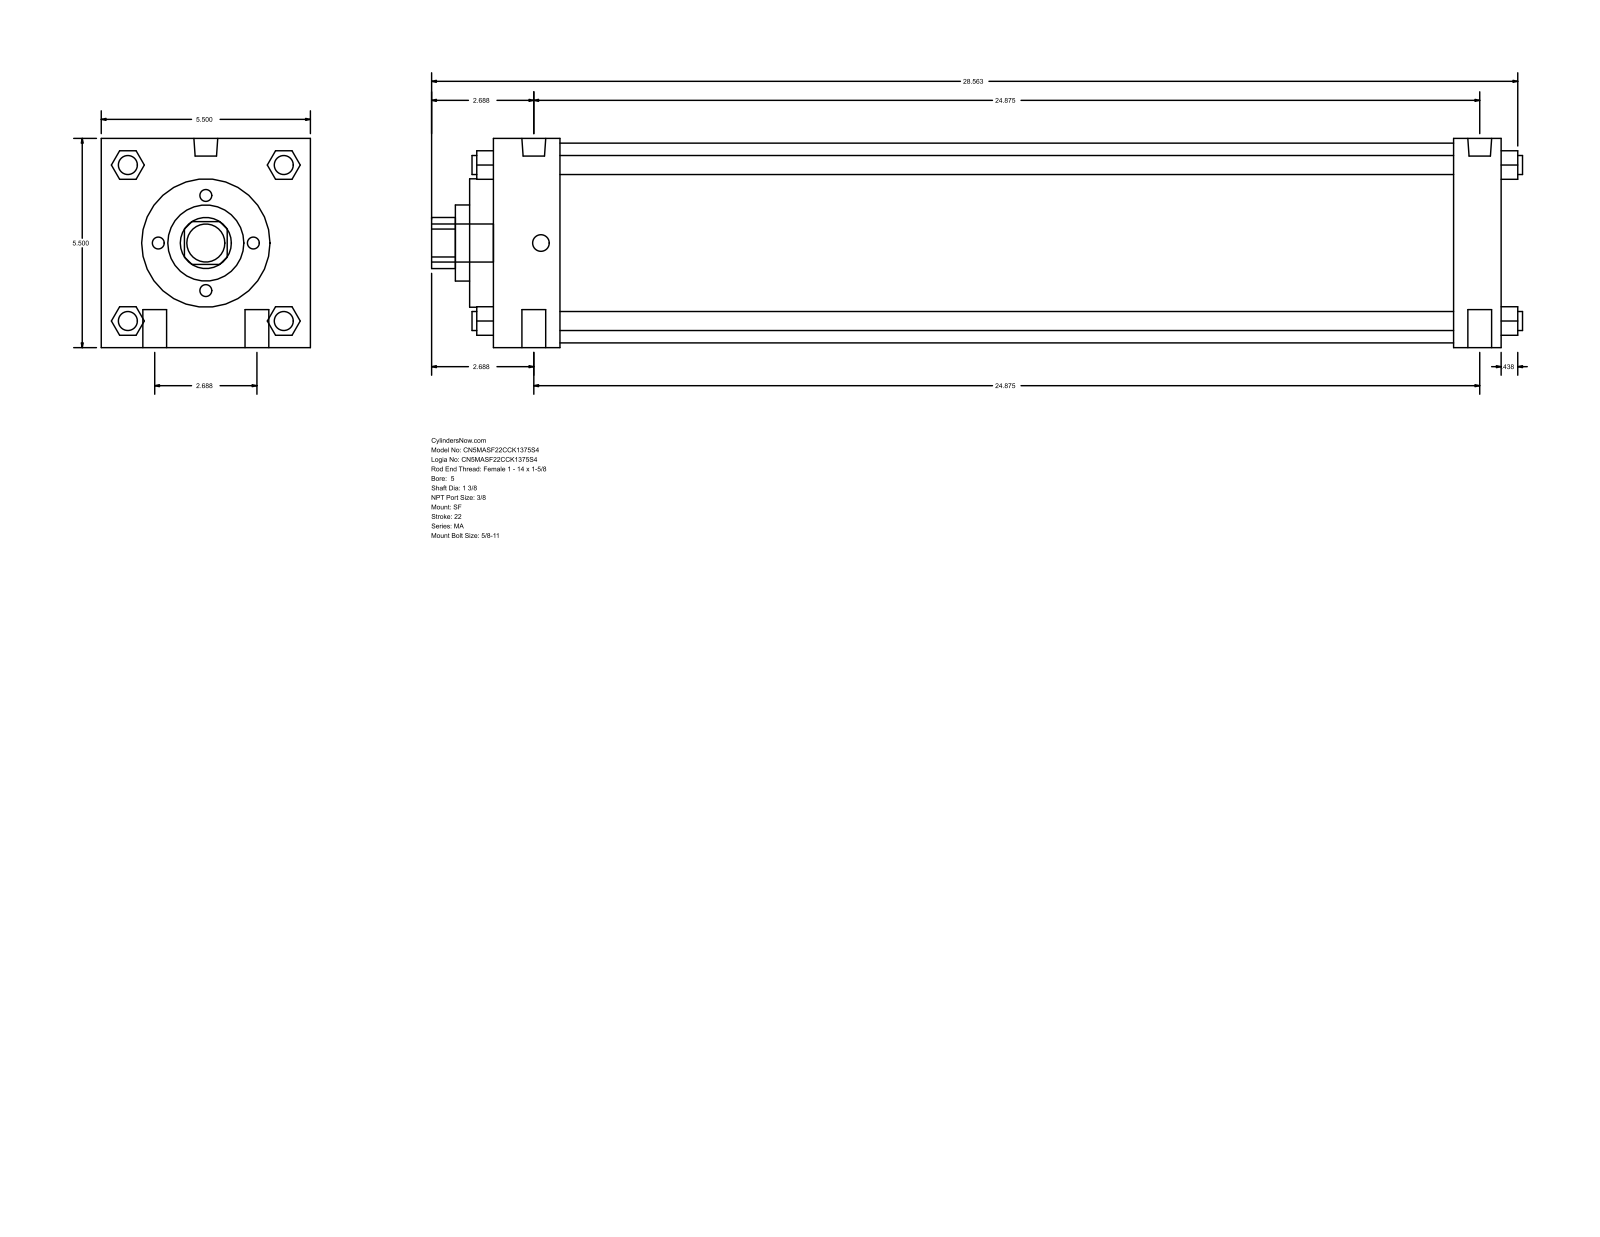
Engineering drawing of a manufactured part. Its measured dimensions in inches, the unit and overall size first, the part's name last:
Units: inches
Overall size (bounding box): 28.687 × 5.5 × 5.5
Round holes (diameter × count): ⌀1.375 ×1, ⌀2 ×1, ⌀3.375 ×1, ⌀5.25 ×1
Round bosses / shafts (diameter × count): ⌀0.625 ×4, ⌀0.5 ×4, ⌀0.627 ×2, ⌀0.437 ×2, ⌀1 ×1
Partial cylindrical surfaces — rounded edges, fillets, slot ends (radius × count): R0.672 ×1
Main face-to-face distances: 5.5, 26.5, 1.75, 25.25, 23.5, 24.75, 1.25, 0.625, 2.375, 25.875
Bodies: 0 solids, 126 faces (95 planar, 31 cylindrical, 0 other)
Part name (STEP PRODUCT): MA_SF__0500_1.375
STEP written by: GSSL Pune (CONFIG_CONTROL_DESIGN)
